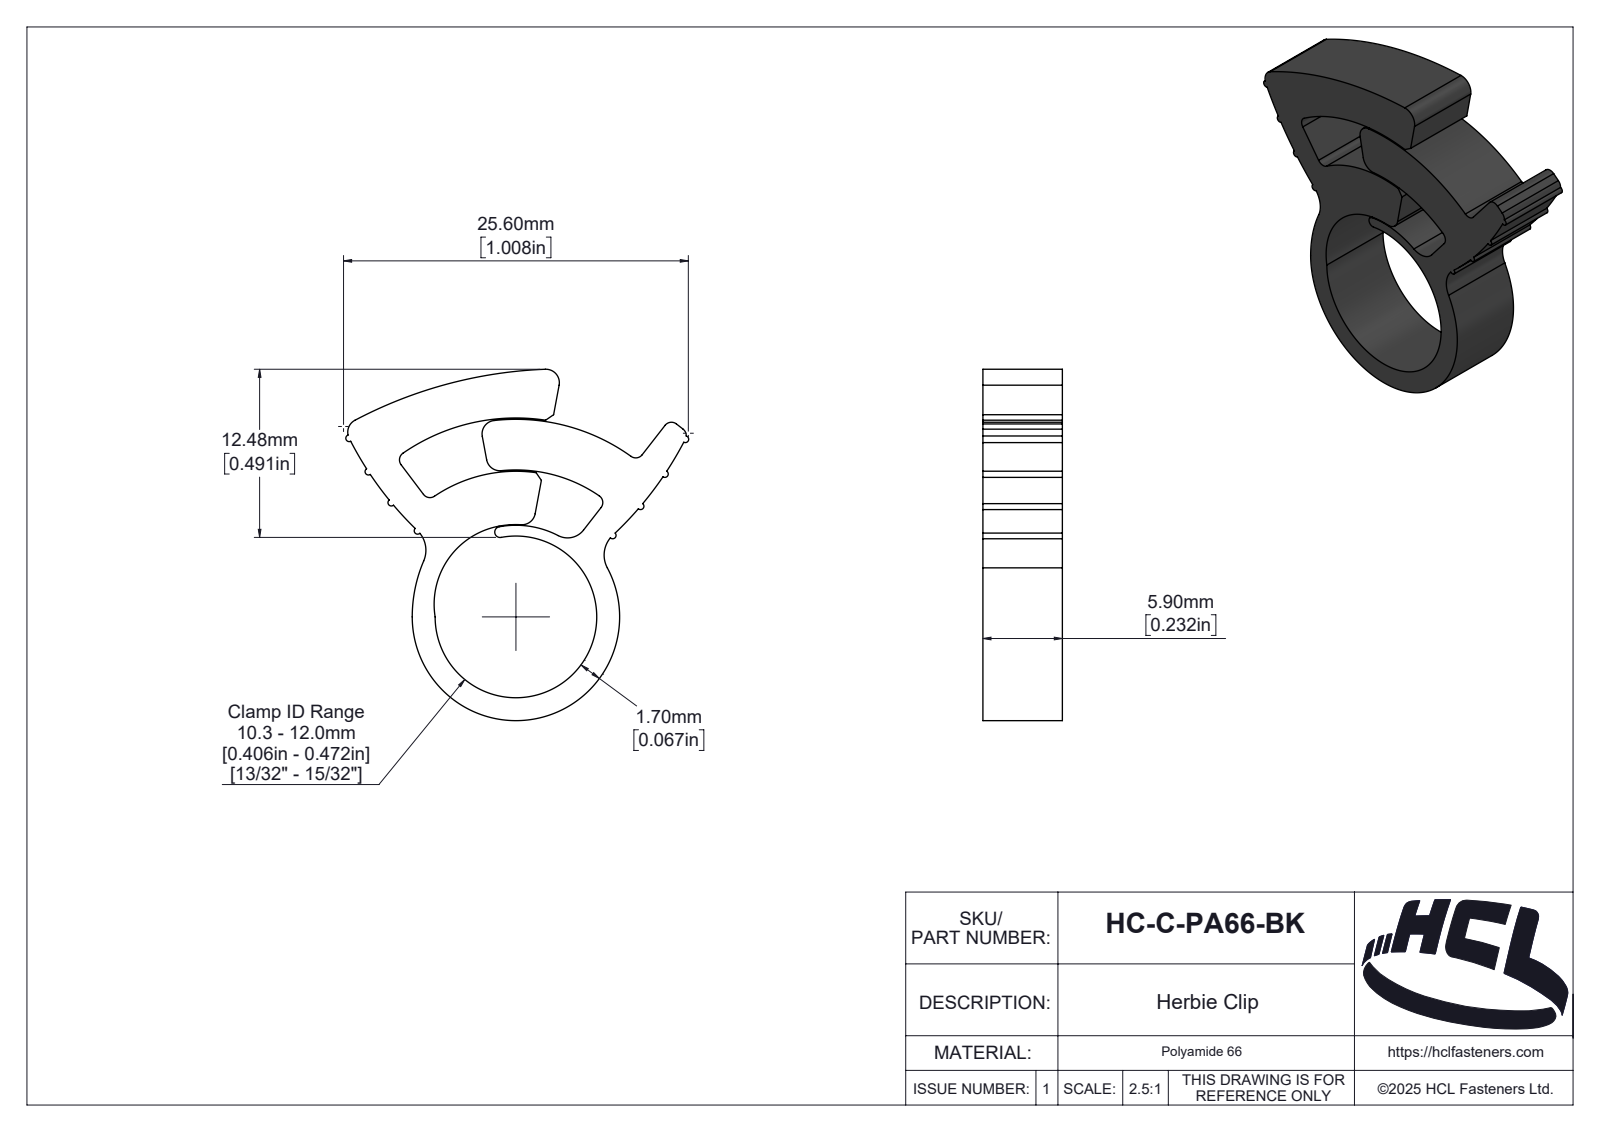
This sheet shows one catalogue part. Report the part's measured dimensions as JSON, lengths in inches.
{"part_name": "HC-C-PA66-BK", "step_written_by": "SolidWorks 2025 (AUTOMOTIVE_DESIGN)", "units": "inches", "bodies": {"solids": 1, "faces": 162, "planar": 13, "cylindrical": 100, "other": 49}, "overall_size": [1.027, 1.002, 0.232], "volume_in3": 0.081, "surface_area_in2": 2.416, "partial_cylinders_radius": [[0.01, 8], [0.024, 6], [0.039, 5], [0.079, 2], [0.007, 1], [0.016, 1], [0.026, 1], [0.033, 1]], "face_to_face_distances": [0.232]}
